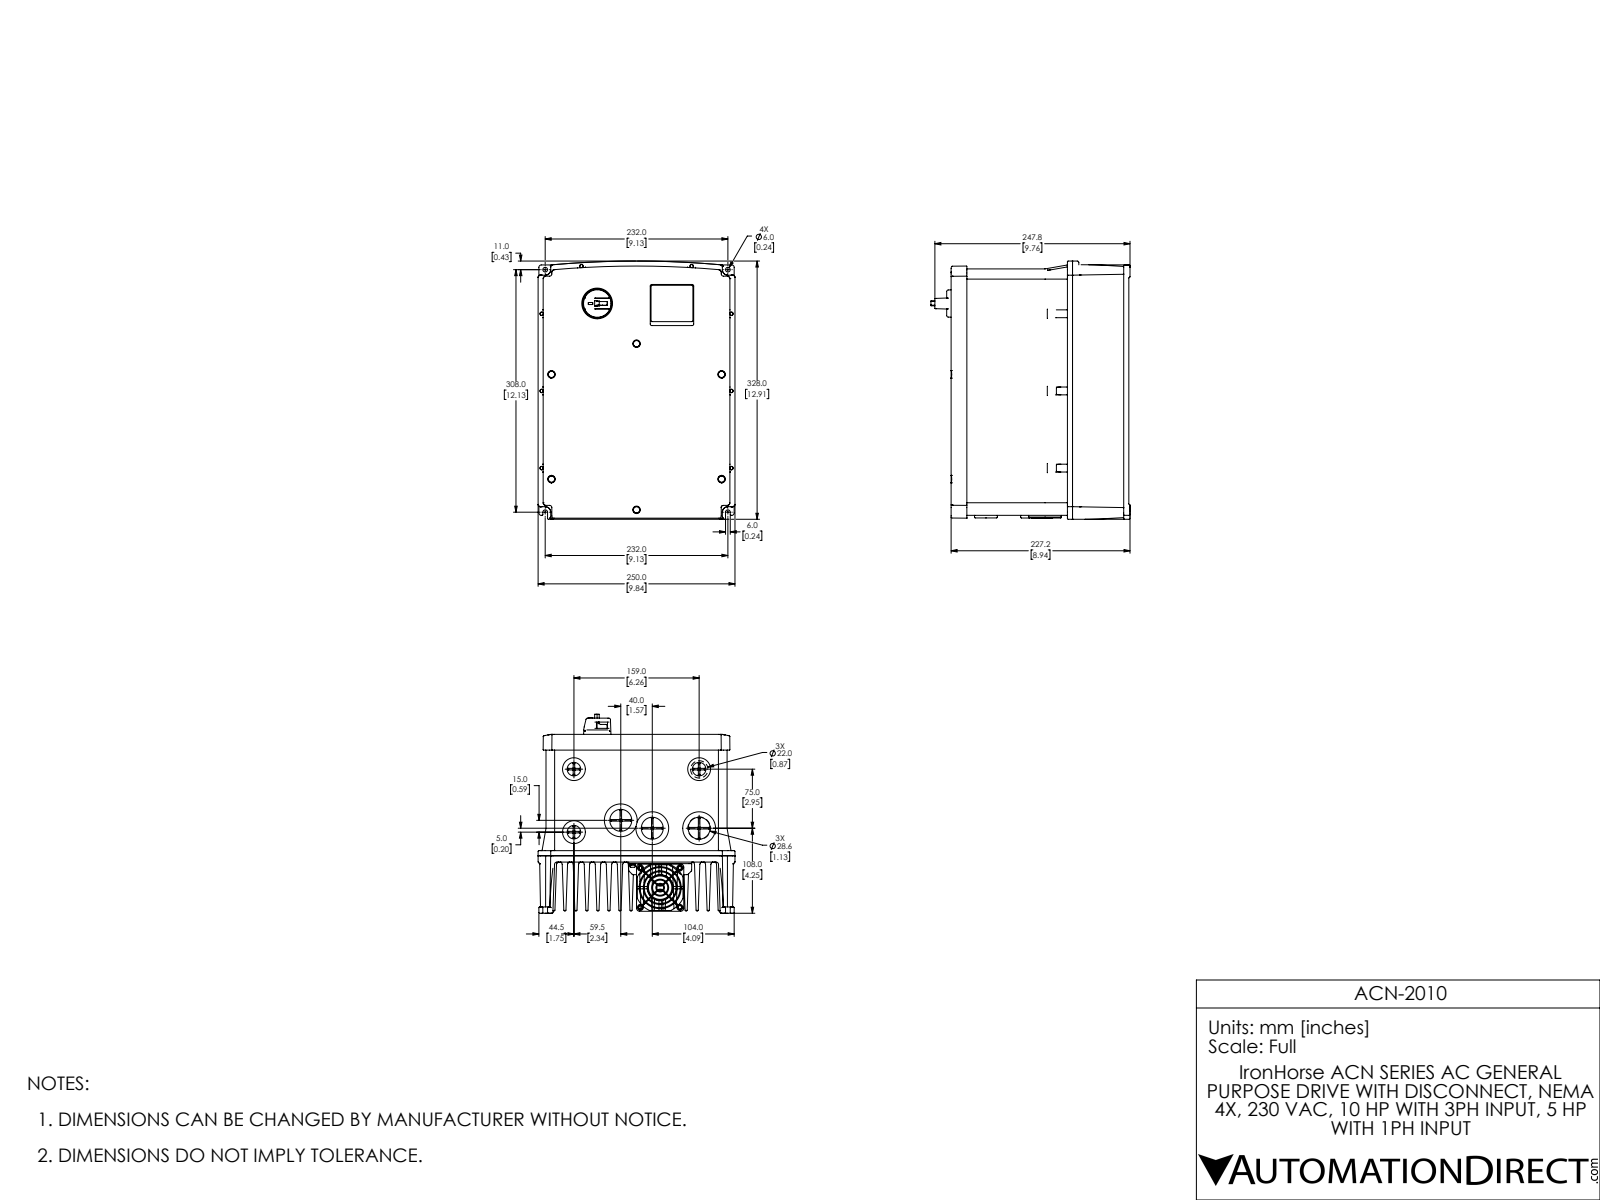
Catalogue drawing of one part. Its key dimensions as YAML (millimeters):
part_name: "total_075_v2_assy_asm red surfs r1 red 3 combined from NON PDS 3F Ext Comb 1 w PLUGSb"
step_written_by: "SolidWorks 2017 (AUTOMOTIVE_DESIGN)"
units: millimeters
bodies: {solids: 11, faces: 4345, planar: 1279, cylindrical: 1598, other: 1468}
overall_size: [327.96, 252.8, 250]
volume: 11240000
surface_area: 1283000
round_holes:
  - {diameter: 4, count: 43}
  - {diameter: 4.5, count: 22}
  - {diameter: 7.1, count: 8}
  - {diameter: 8.5, count: 6}
  - {diameter: 5, count: 3}
  - {diameter: 17.2, count: 3}
  - {diameter: 22, count: 3}
  - {diameter: 26, count: 3}
  - {diameter: 27.9, count: 3}
  - {diameter: 6, count: 2}
  - {diameter: 29.5, count: 2}
  - {diameter: 38.7, count: 2}
round_bosses_or_shafts:
  - {diameter: 8, count: 14}
  - {diameter: 1.2, count: 11}
  - {diameter: 9, count: 8}
  - {diameter: 41.7, count: 3}
  - {diameter: 34.3, count: 3}
  - {diameter: 29, count: 3}
  - {diameter: 21.6, count: 3}
  - {diameter: 33, count: 2}
partial_cylinders:
  - {radius: 1, count: 229}
  - {radius: 0.5, count: 185}
  - {radius: 3, count: 104}
  - {radius: 2, count: 77}
  - {radius: 0.3, count: 60}
  - {radius: 2.2, count: 28}
  - {radius: 2.8, count: 28}
  - {radius: 0.2, count: 13}
face_to_face_distances: [27.97, 41.96, 69.93, 13.99, 55.94, 111.89, 97.9, 13.98, 83.92, 139.86]
hole_center_spacings: [35.36, 50, 80.82, 70.71, 244.55, 16.5, 29.15, 37.85]
